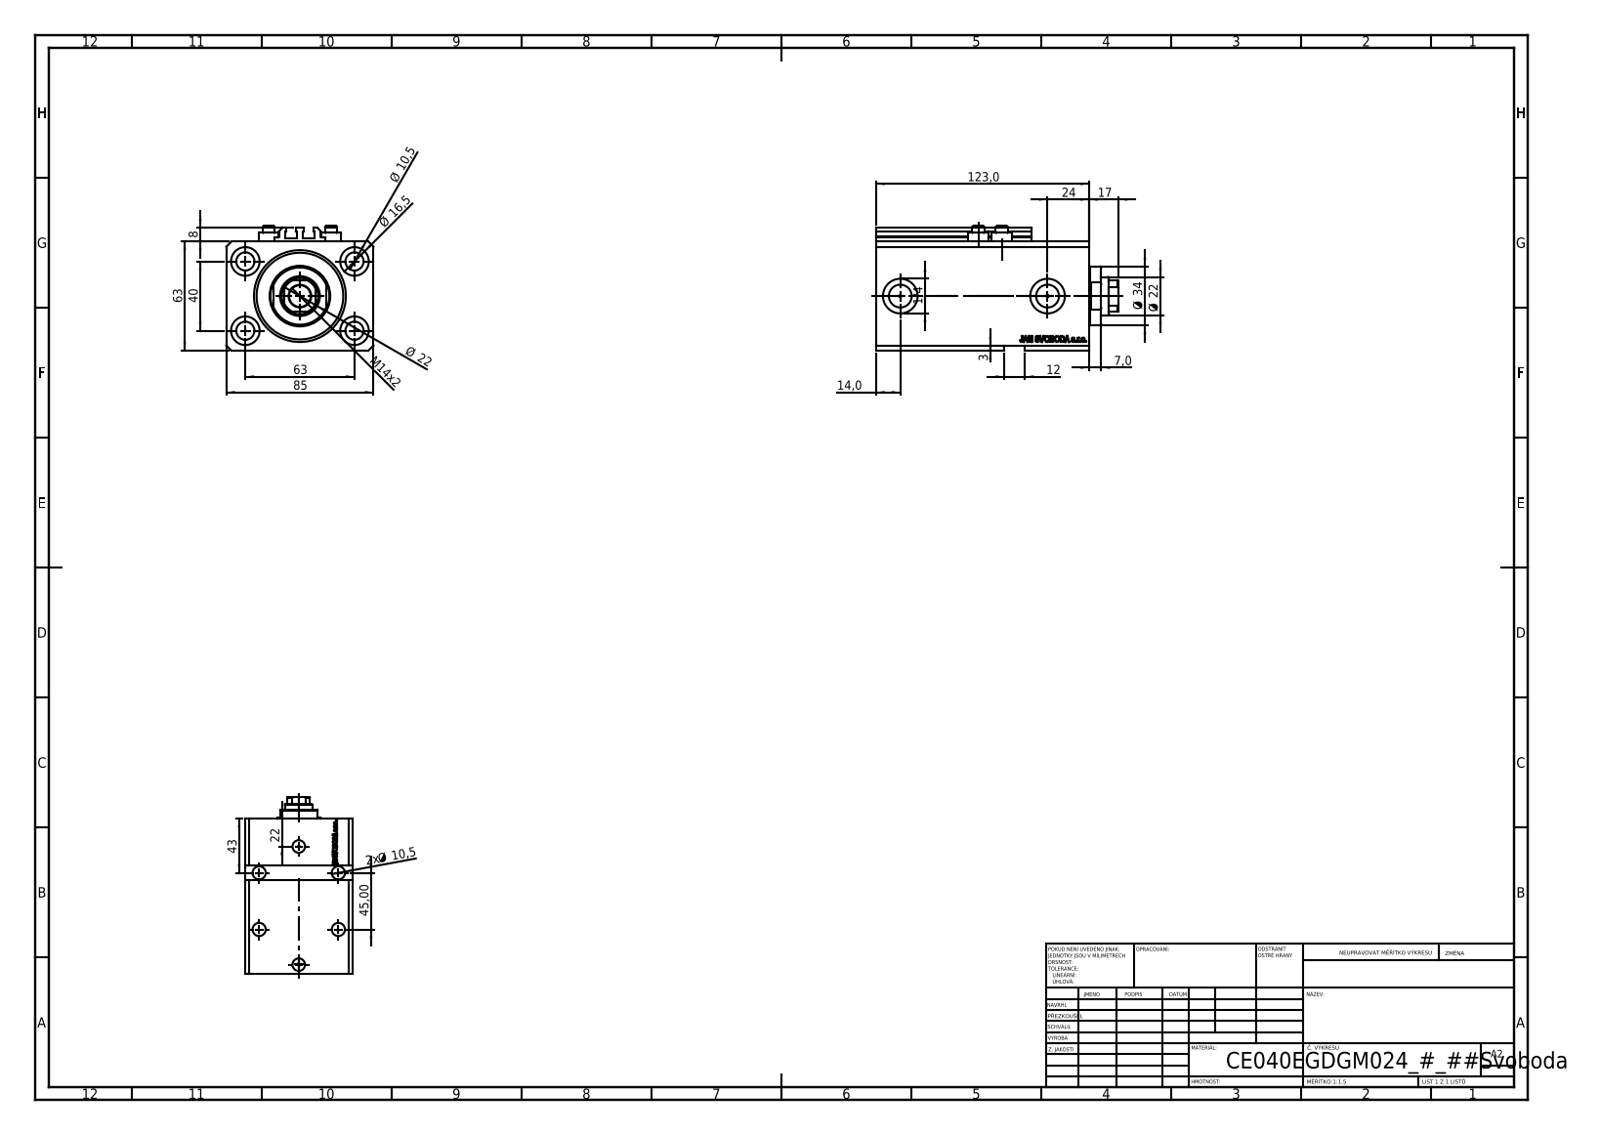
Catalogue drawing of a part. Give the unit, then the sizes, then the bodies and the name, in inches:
Units: inches
Overall size (bounding box): 5.512 × 3.346 × 2.835
Round holes (diameter × count): ⌀0.413 ×8, ⌀0.049 ×4, ⌀0.157 ×4, ⌀0.65 ×4, ⌀0.394 ×2, ⌀0.518 ×2, ⌀0.787 ×2, ⌀0.492 ×1, ⌀0.866 ×1, ⌀1.575 ×1, ⌀2.087 ×1
Round bosses / shafts (diameter × count): ⌀0.457 ×4, ⌀0.276 ×4, ⌀1.339 ×1
Partial cylindrical surfaces — rounded edges, fillets, slot ends (radius × count): R0.008 ×10, R0.413 ×1
Main face-to-face distances: 2.48, 3.346, 4.843, 0.669, 4.173, 0.449, 3.724, 4.394, 0.118, 2.205
Hole centre spacings: 1.469, 2.48, 0.535, 0.606, 0.983, 1.084, 1.324, 1.417
Volume: 33.75 in³ · Surface area: 186.8 in²
Bodies: 8 solids, 1123 faces (539 planar, 158 cylindrical, 426 other)
Part name (STEP PRODUCT): V250CE_VC_E; V250CE_E_Body; ALLEN BOLT V250CE; V250CE_C_VCP
STEP written by: SolidWorks 2019 (CONFIG_CONTROL_DESIGN)
